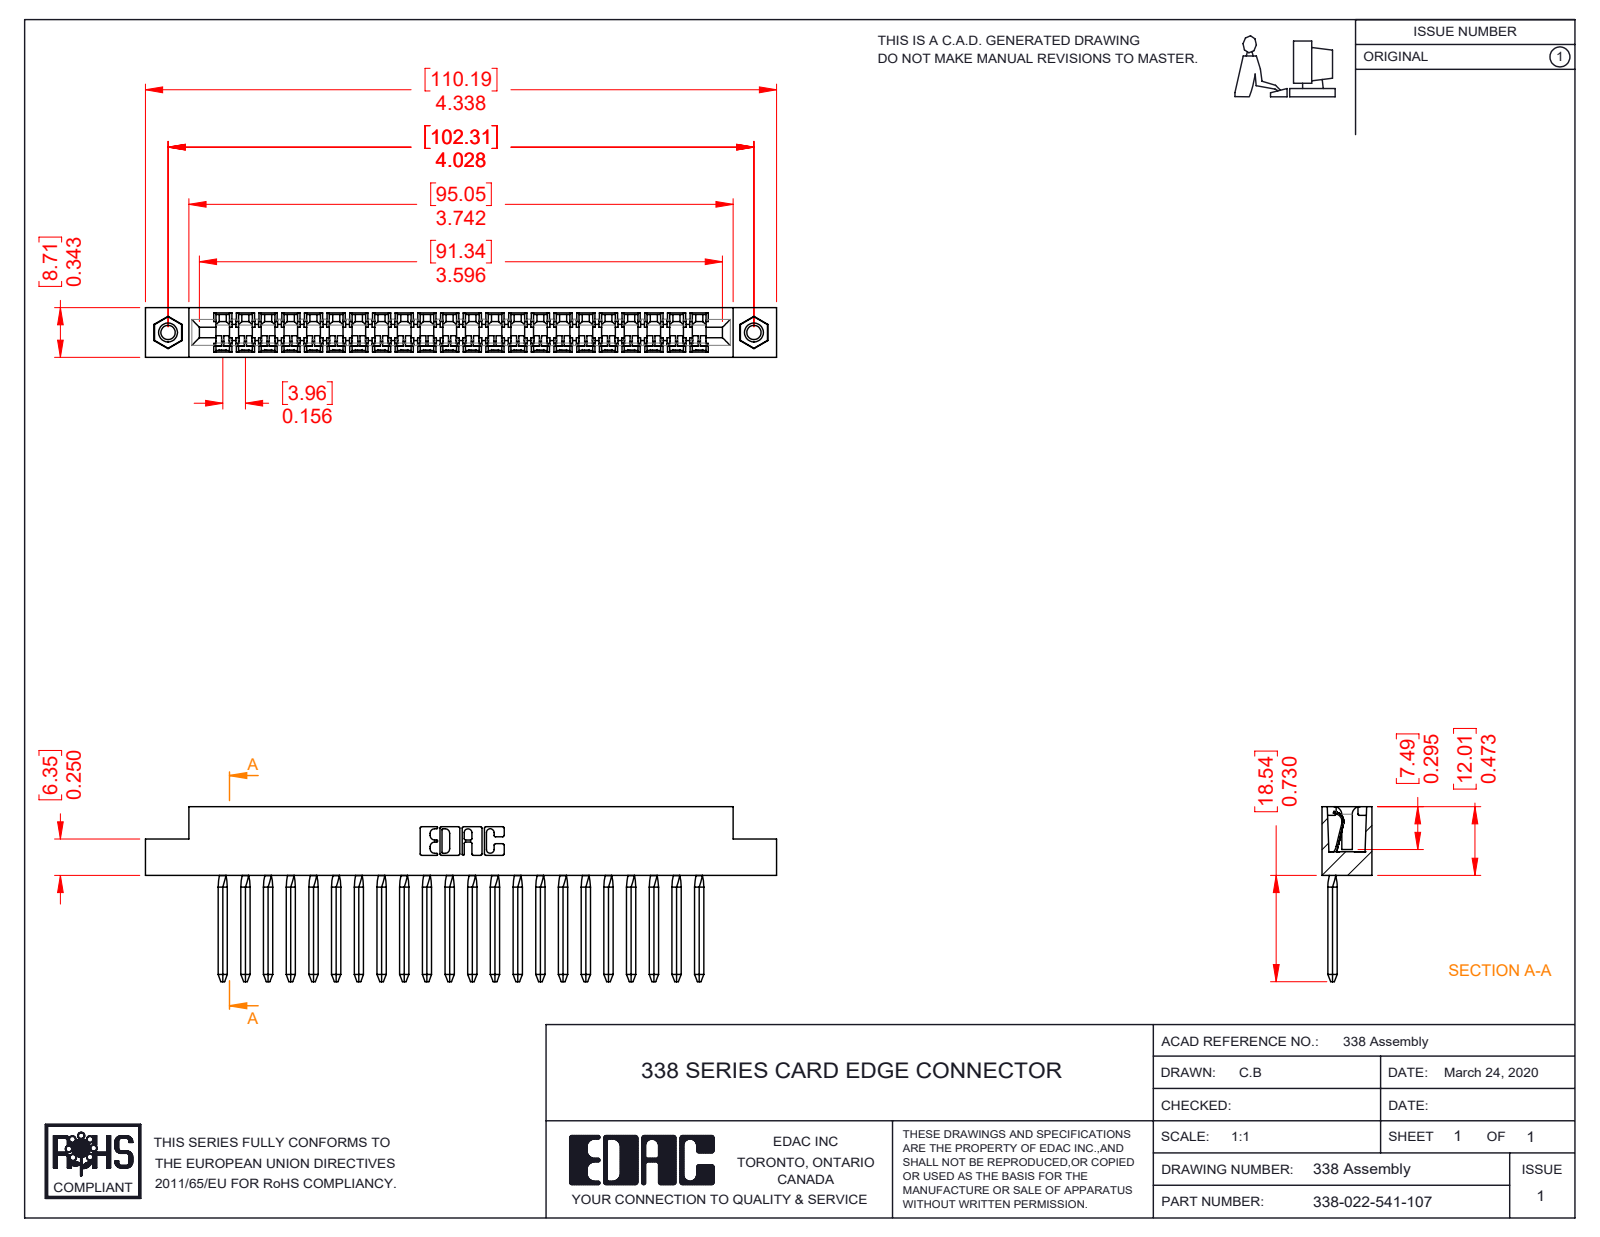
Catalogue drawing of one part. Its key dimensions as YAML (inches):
part_name: "338-290-001_541; 338-210-001_338-210-022-004; 338-022-541-107; 345-250-001_345-250-005-103"
step_written_by: "SolidWorks 2016 (CONFIG_CONTROL_DESIGN)"
units: inches
bodies: {solids: 25, faces: 2200, planar: 1512, cylindrical: 584, other: 104}
overall_size: [4.338, 1.203, 0.343]
volume: 0.47
surface_area: 19.28
round_holes:
  - {diameter: 0.098, count: 2}
  - {diameter: 0.125, count: 2}
  - {diameter: 0.156, count: 2}
round_bosses_or_shafts:
  - {diameter: 0.155, count: 2}
partial_cylinders:
  - {radius: 0.025, count: 90}
  - {radius: 0.008, count: 22}
  - {radius: 0.01, count: 22}
  - {radius: 0.055, count: 18}
  - {radius: 0.067, count: 18}
  - {radius: 0.1, count: 17}
  - {radius: 0.007, count: 6}
  - {radius: 0.031, count: 6}
face_to_face_distances: [0.343, 0.156, 0.11, 0.624, 0.207, 0.135, 0.78, 0.468, 0.221, 0.312]
hole_center_spacings: [4.028]
